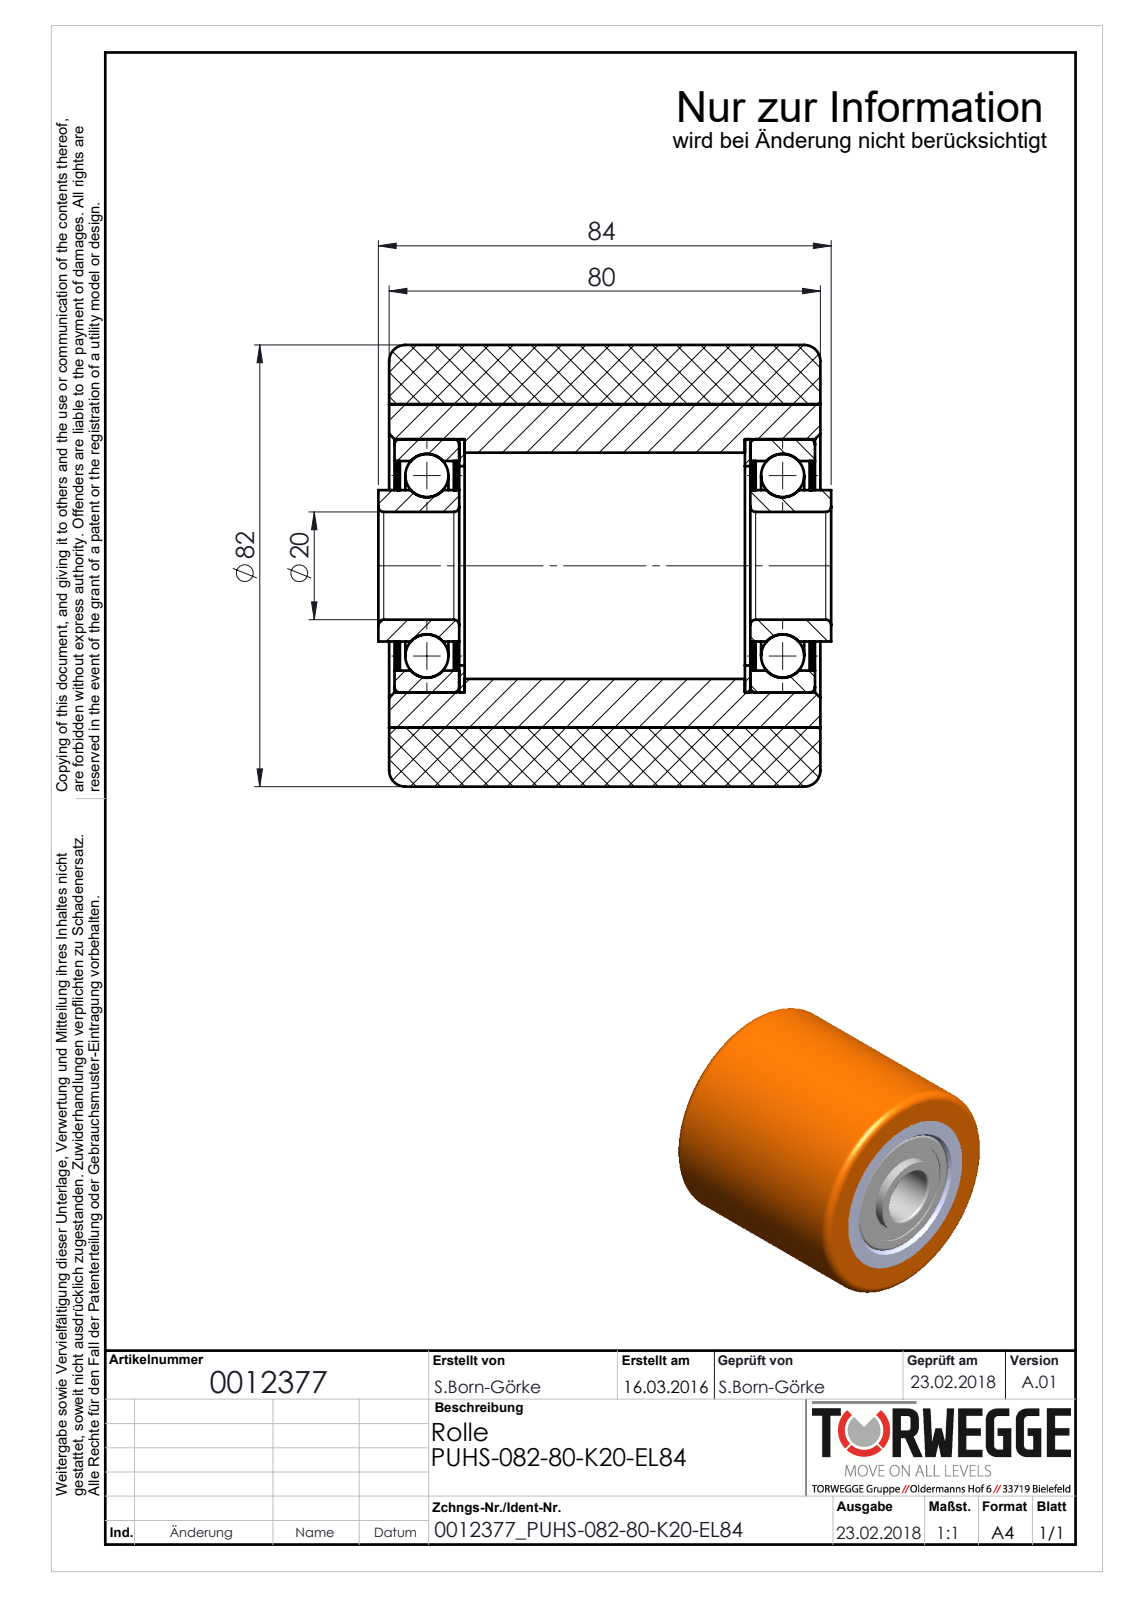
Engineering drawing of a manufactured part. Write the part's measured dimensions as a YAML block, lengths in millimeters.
part_name: "0012377_PUHS-082-80-K20-EL84"
step_written_by: "SolidWorks 2016 (AUTOMOTIVE_DESIGN)"
units: millimeters
bodies: {solids: 0, faces: 54, planar: 10, cylindrical: 24, other: 20}
overall_size: [84, 82, 82]
round_holes:
  - {diameter: 20, count: 1}
  - {diameter: 38.9, count: 1}
  - {diameter: 42, count: 1}
  - {diameter: 47, count: 1}
  - {diameter: 60, count: 1}
round_bosses_or_shafts:
  - {diameter: 82, count: 1}
  - {diameter: 28.1, count: 1}
face_to_face_distances: [80, 1.5, 78.5, 1, 79, 0.5, 77.5, 77, 2, 3]
